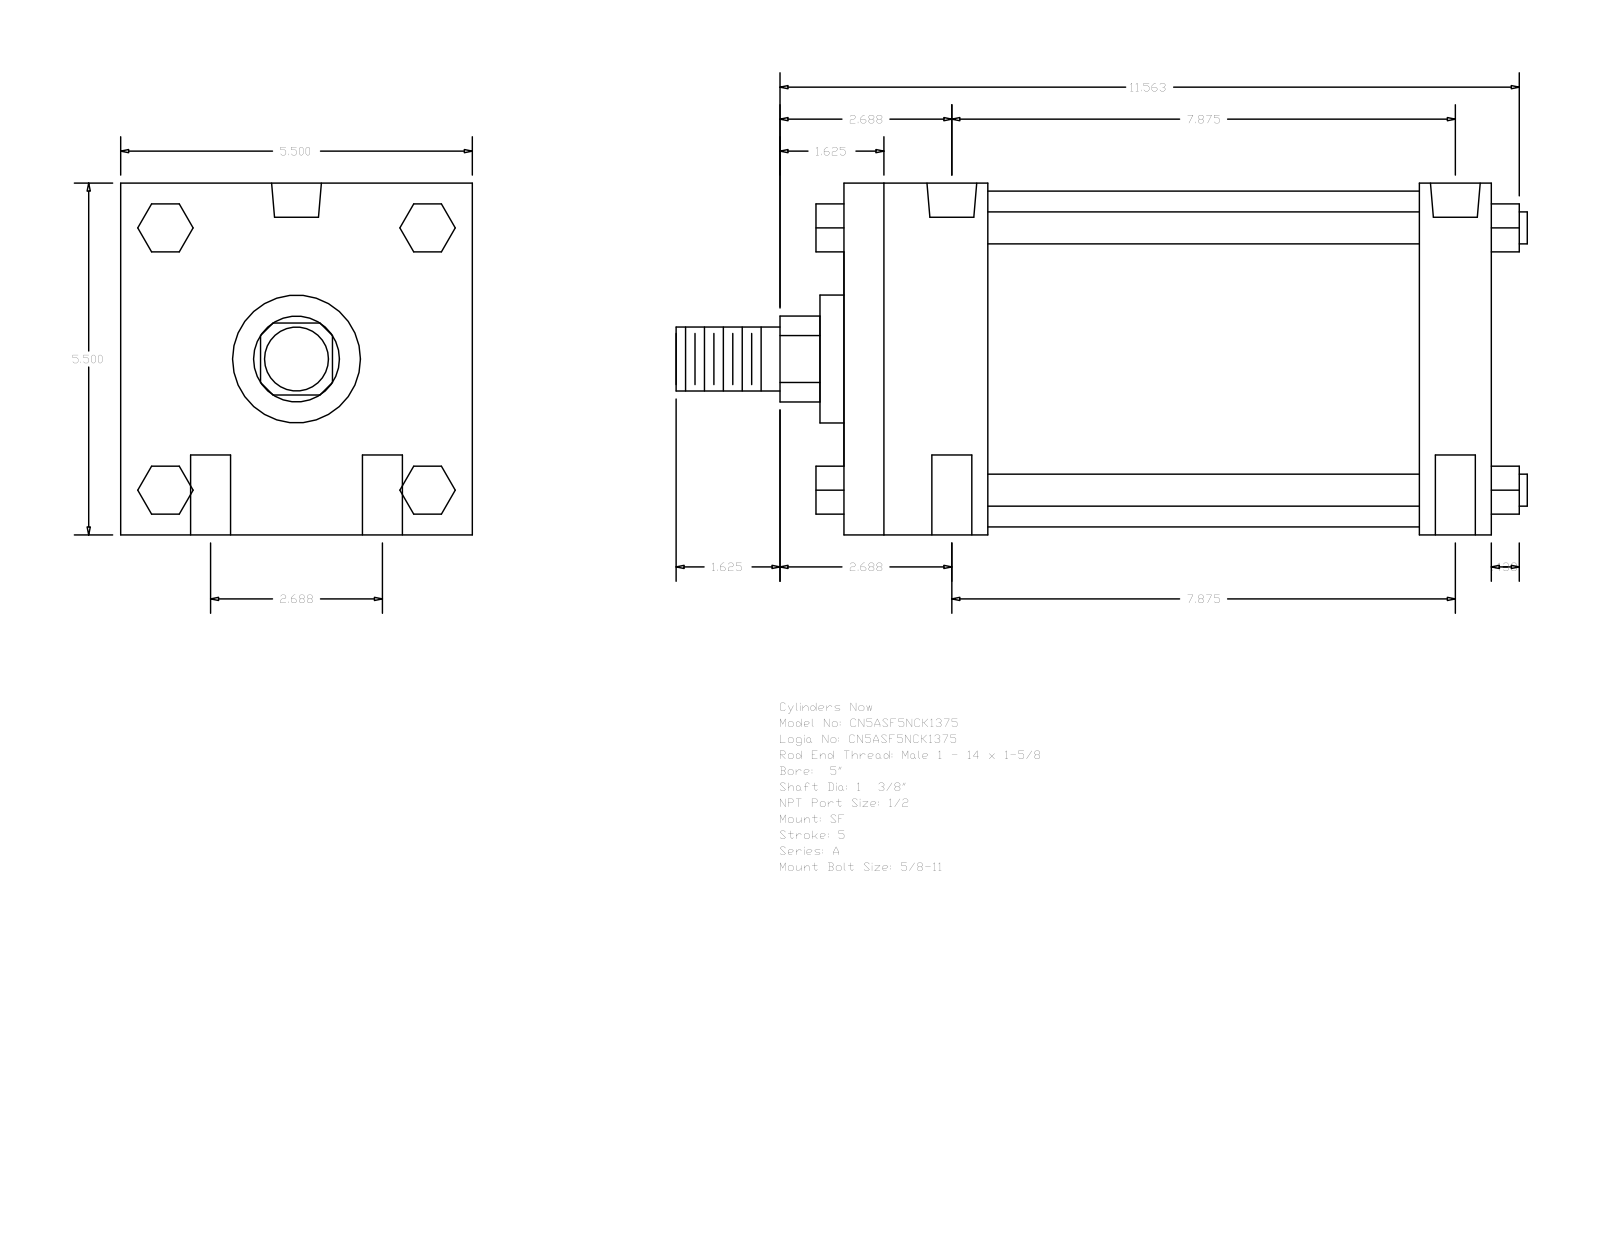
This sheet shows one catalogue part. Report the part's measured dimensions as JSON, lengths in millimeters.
{"part_name": "A_SF__0500_1.375", "step_written_by": "GSSL Pune (CONFIG_CONTROL_DESIGN)", "units": "millimeters", "bodies": {"solids": 0, "faces": 124, "planar": 94, "cylindrical": 30, "other": 0}, "overall_size": [338.14, 139.7, 139.7], "round_holes": [[15.88, 4], [8.73, 2], [19.77, 2]], "round_bosses_or_shafts": [[12.7, 4], [133.35, 1], [50.8, 1], [34.92, 1], [25.4, 1]], "partial_cylinders_radius": [[17.06, 1]], "face_to_face_distances": [139.7, 257.17, 57.15, 228.6, 171.45, 200.02, 28.57, 19.05, 52.07, 90.18], "hole_center_spacings": [34.13, 202.92, 200.03, 68.26, 211.36, 195.25]}
